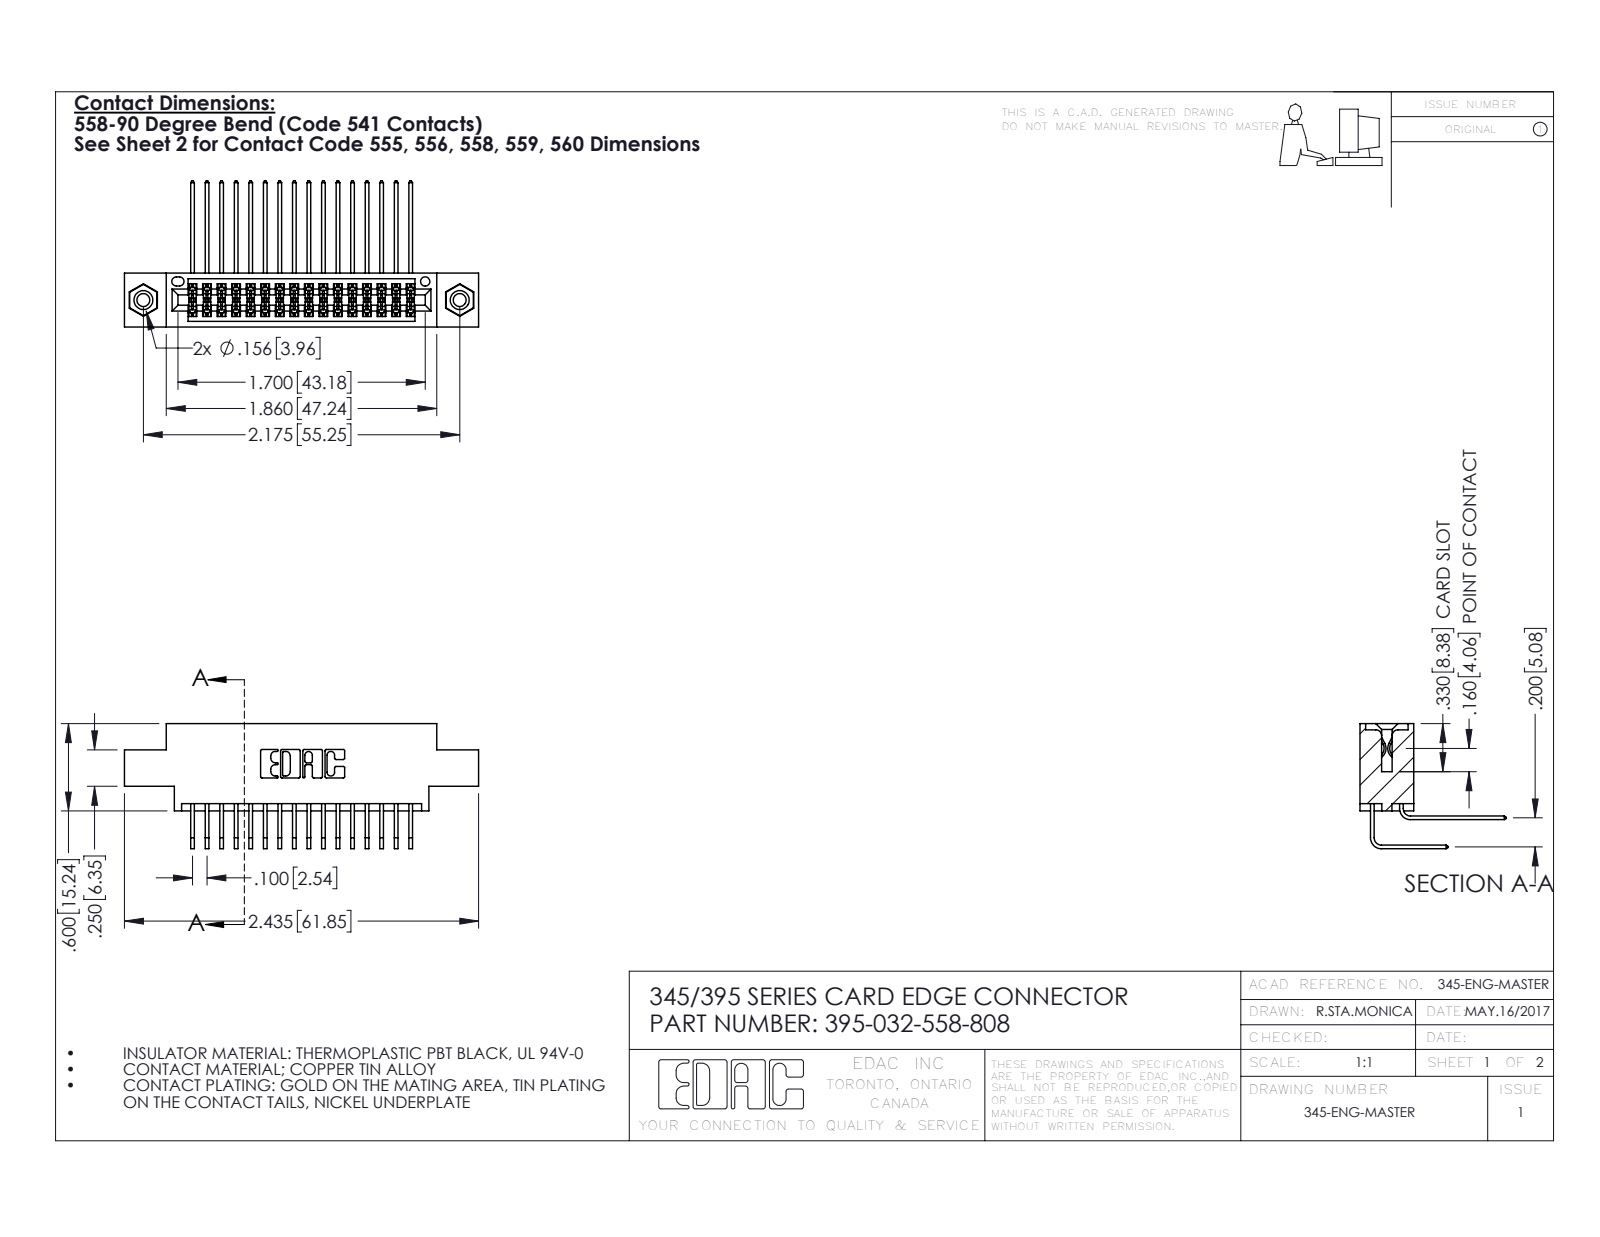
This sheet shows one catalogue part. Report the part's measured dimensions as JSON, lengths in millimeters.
{"part_name": "345-292-001_558 559 Tail - 1; 395-032-558-808; 345-292-001_558 Tail - 2; 345-250-001_345-250-003-102 (+1 more)", "step_written_by": "SolidWorks 2016 (CONFIG_CONTROL_DESIGN)", "units": "millimeters", "bodies": {"solids": 35, "faces": 1854, "planar": 1236, "cylindrical": 602, "other": 16}, "overall_size": [61.8, 25.5, 21.8], "volume_mm3": 5830, "surface_area_mm2": 9142, "round_holes": [[2.3, 2], [3.2, 2], [4, 2], [1.6, 1]], "round_bosses_or_shafts": [[3.9, 2]], "partial_cylinders_radius": [[0.2, 49], [0.3, 22], [0.2, 6], [0.8, 6], [0.7, 3], [0.4, 2], [0.5, 2], [0.6, 2]], "face_to_face_distances": [5.1, 1.8, 7.6, 9.4, 2.5, 6.9, 0.6, 5.7, 2.5, 4.4], "hole_center_spacings": [6.9, 49.3, 55.2]}
